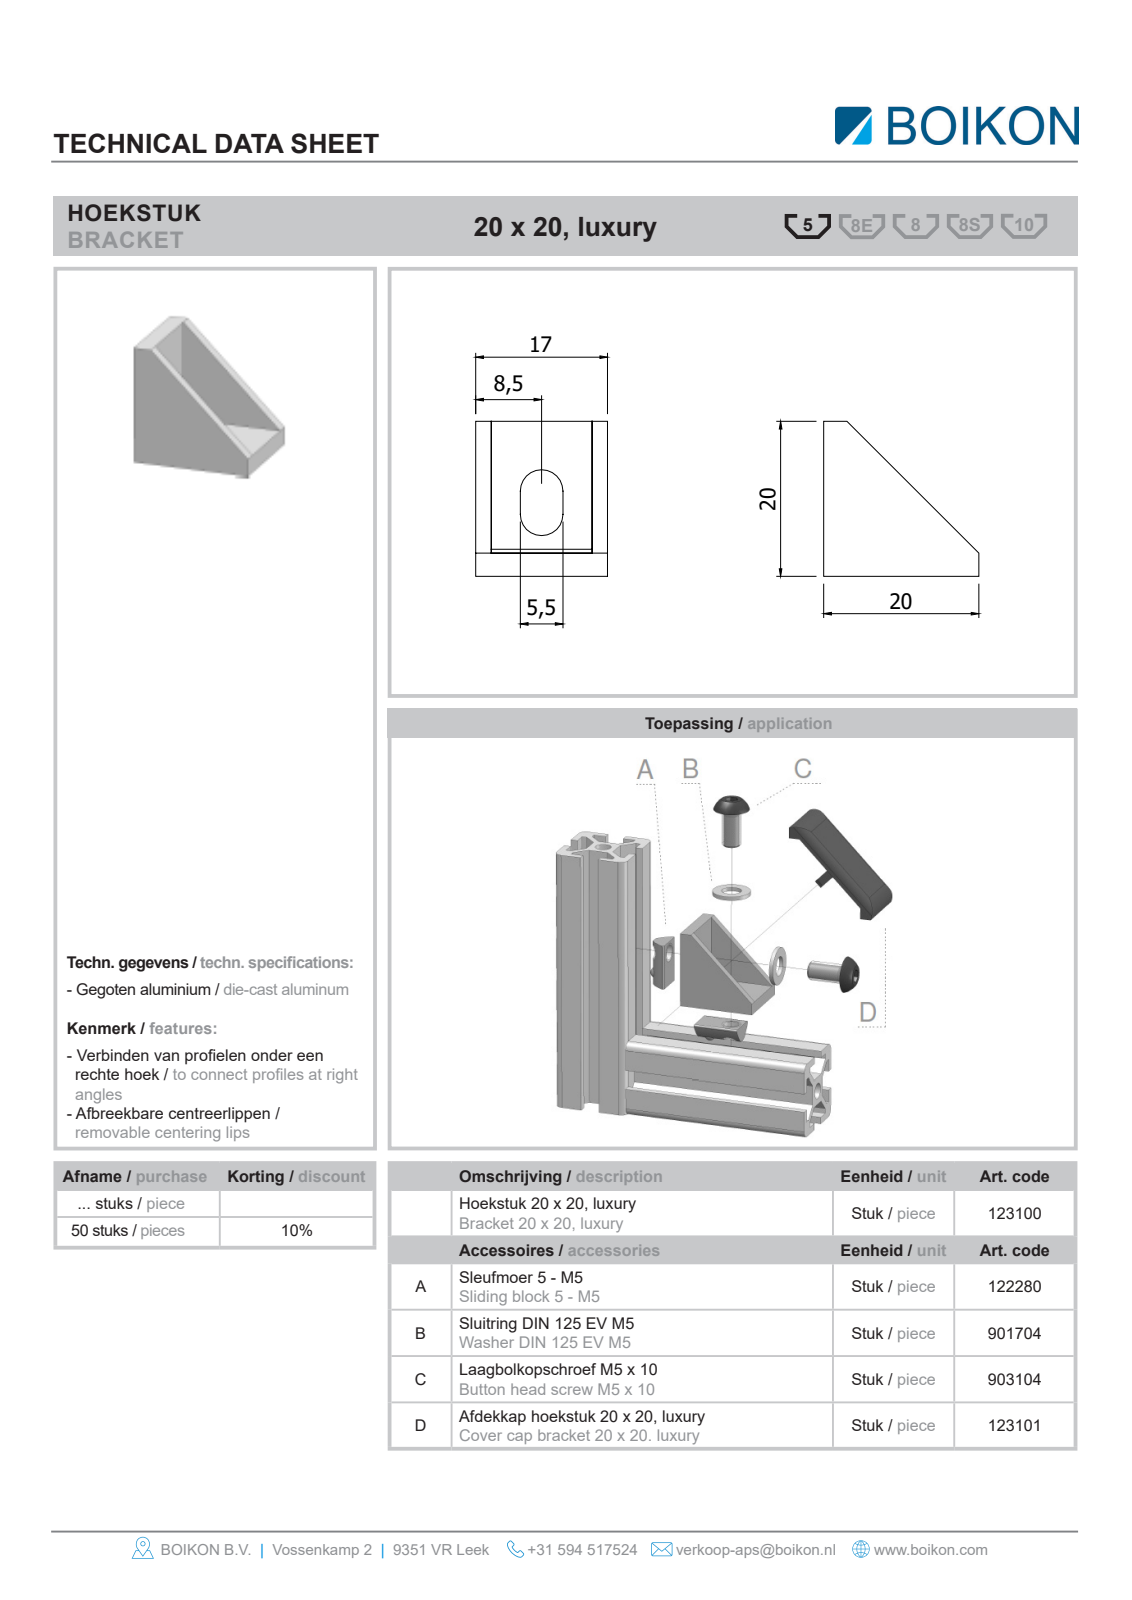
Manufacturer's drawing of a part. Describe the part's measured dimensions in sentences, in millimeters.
The part is named "Root; 123100HOEKSTUK 20X20 LUXURYBOIKON; 123101AFDEKKAP HOEKSTUK 20X20 LUXURYBOIKON; 122280Sleufmoer 5 - M5 met kogelBOIKON (+2 more)". Its 3-D file was written by "HiCAD 2013 1802.4 Build 509 (AUTOMOTIVE_DESIGN)". It is 8 solids with 146 faces: 93 planar, 45 cylindrical and 8 other. Overall it measures 29.94 by 29.94 by 17 millimeters. Its volume is 4 469 cubic millimeters and its surface area 5 239 square millimeters. Round holes: 2 of diameter 2.96, 2 of diameter 5, 2 of diameter 5.3. Round bosses or shafts: 2 of diameter 10, 2 of diameter 4.02. Partial cylindrical surfaces (rounded edges, fillets, slot ends): 4 of radius 0.4, 4 of radius 0.7, 4 of radius 2.75, 4 of radius 8.5, 2 of radius 2, 2 of radius 5, 1 of radius 0.5. The main face-to-face distances are 3, 2, 17, 1, 15, 4, 0.75, 13, 14.25, 1.8. The hole center spacings are 6.
